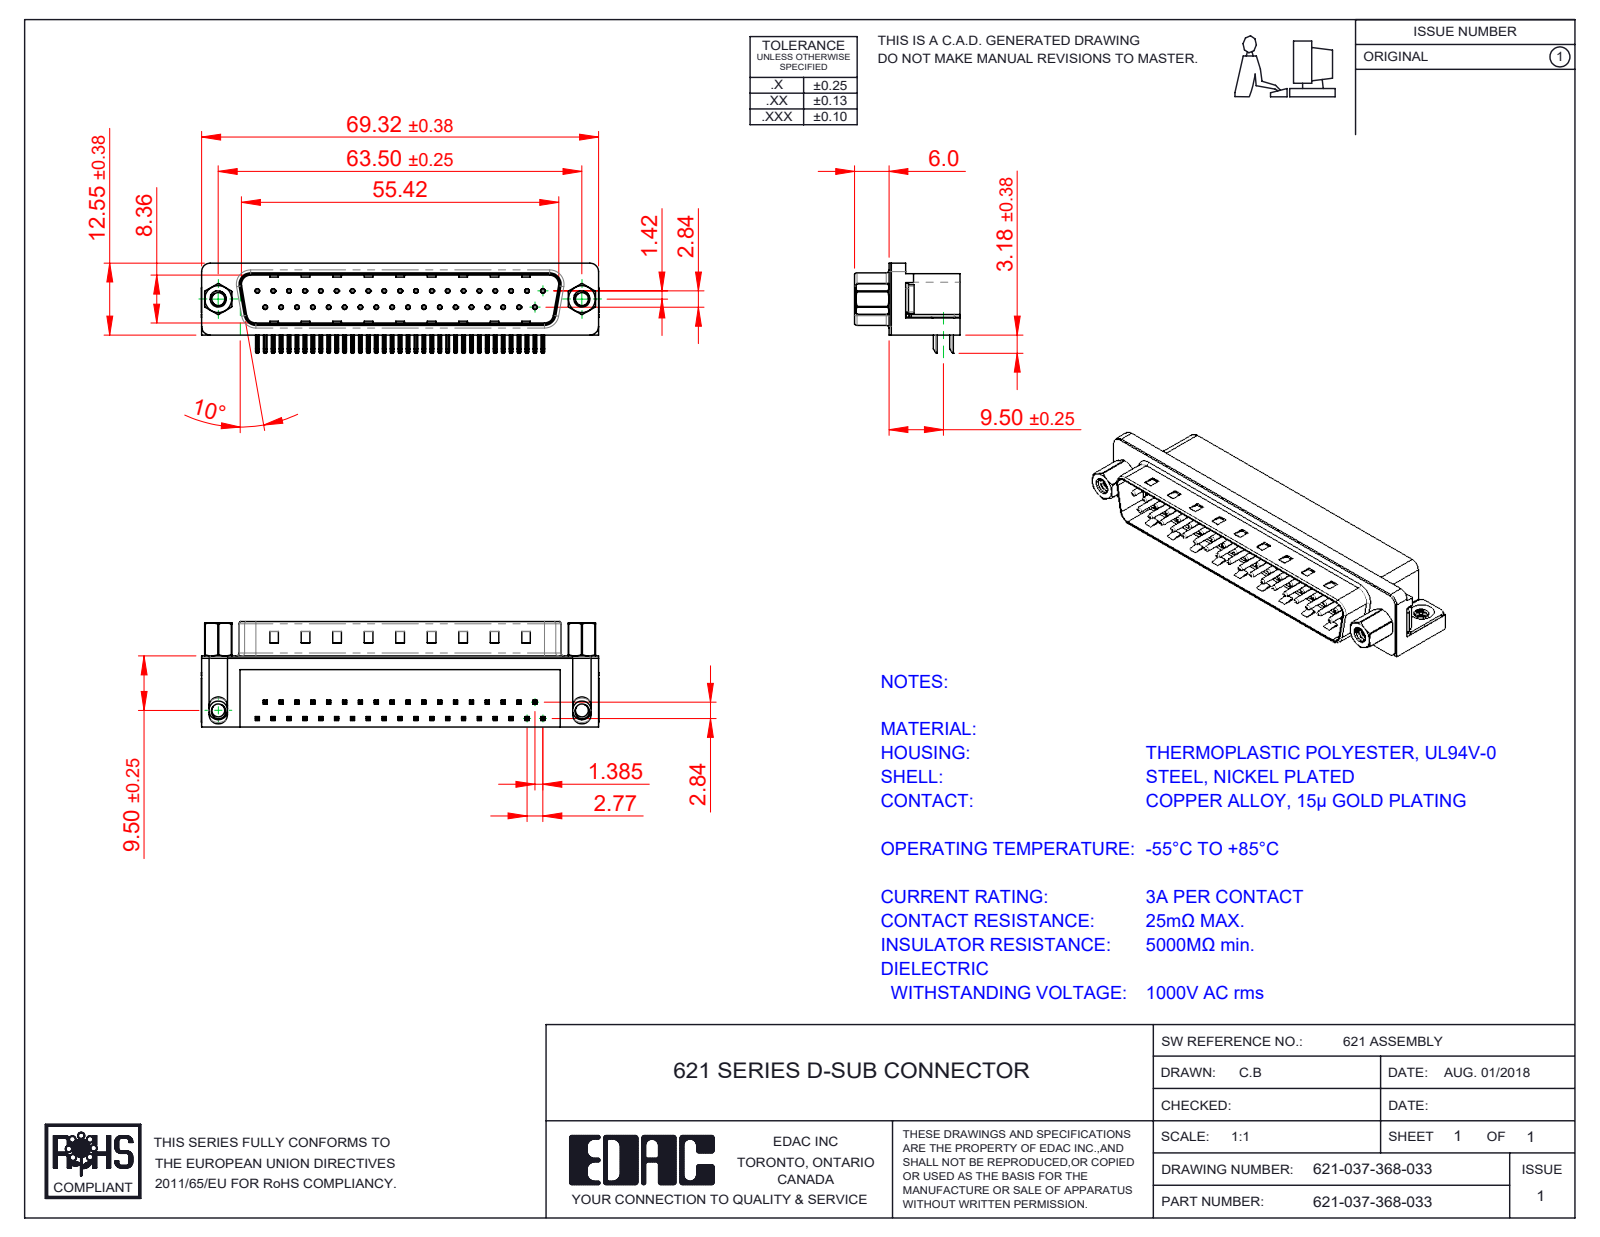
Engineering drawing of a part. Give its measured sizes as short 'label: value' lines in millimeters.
name: 621-037-368-033; 621 Shell_37 Socket; 621 2 Prong Board Lock; 621 Housing_37 Socket (+4 more)
written by: SolidWorks 2016 (CONFIG_CONTROL_DESIGN)
unit: mm
bodies: 45 solids, 3365 faces (2067 planar, 995 cylindrical, 303 other)
size: 69.4 × 18.4 × 16.25
volume: 8 834 mm³; area: 10 583 mm²
holes: 37× ⌀0.35, 37× ⌀0.8, 2× ⌀2.26, 2× ⌀2.29, 2× ⌀4, 2× ⌀4.8, 2× ⌀5
bosses: 37× ⌀0.75, 2× ⌀4.9, 2× ⌀4.75, 2× ⌀3.9, 2× ⌀2.79
rounds: 156× R0.25, 74× R0.12, 16× R1, 14× R0.5, 8× R1.6, 7× R1.5, 4× R0.32, 4× R0.9
face distances: 0.4, 12, 10.35, 8.76, 1.7, 2.1, 10.46, 10.86, 12.4, 9
hole spacings: 3.16, 2.77, 5.54, 8.31, 11.08, 13.85, 19.39, 22.16
